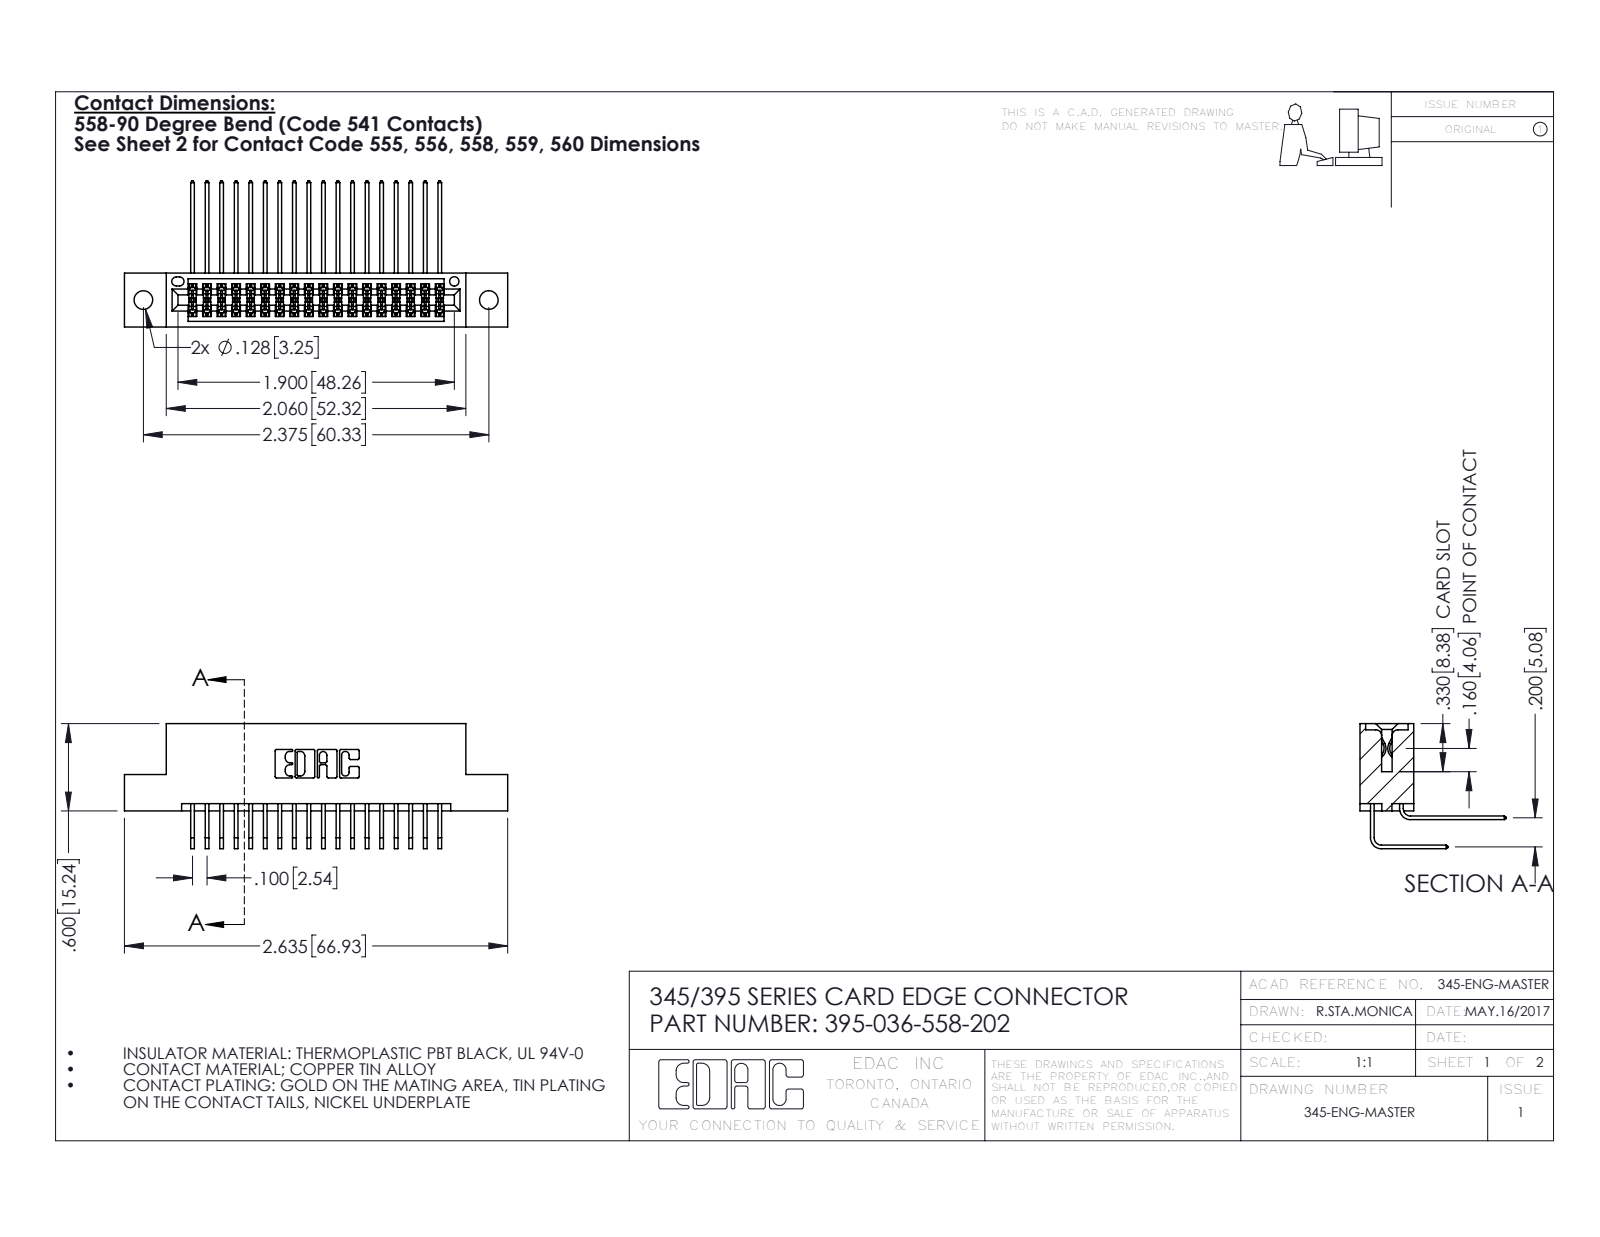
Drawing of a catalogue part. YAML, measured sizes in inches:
part_name: "345-292-001_558 Tail - 2; 345-292-001_558 559 Tail - 1; 345 Part_Flush Mounting Lugs - 0.128 Dia; 395-036-558-202"
step_written_by: "SolidWorks 2016 (CONFIG_CONTROL_DESIGN)"
units: inches
bodies: {solids: 37, faces: 1998, planar: 1340, cylindrical: 658, other: 0}
overall_size: [2.635, 1.005, 0.859]
volume: 0.394
surface_area: 15.15
round_holes:
  - {diameter: 0.128, count: 2}
  - {diameter: 0.064, count: 1}
partial_cylinders:
  - {radius: 0.006, count: 55}
  - {radius: 0.01, count: 22}
  - {radius: 0.007, count: 6}
  - {radius: 0.031, count: 6}
  - {radius: 0.026, count: 3}
  - {radius: 0.014, count: 2}
  - {radius: 0.019, count: 2}
  - {radius: 0.022, count: 2}
face_to_face_distances: [0.2, 0.072, 0.298, 0.37, 0.098, 0.272, 0.025, 0.225, 0.285, 0.1]
hole_center_spacings: [0.27, 2.141, 2.375]
